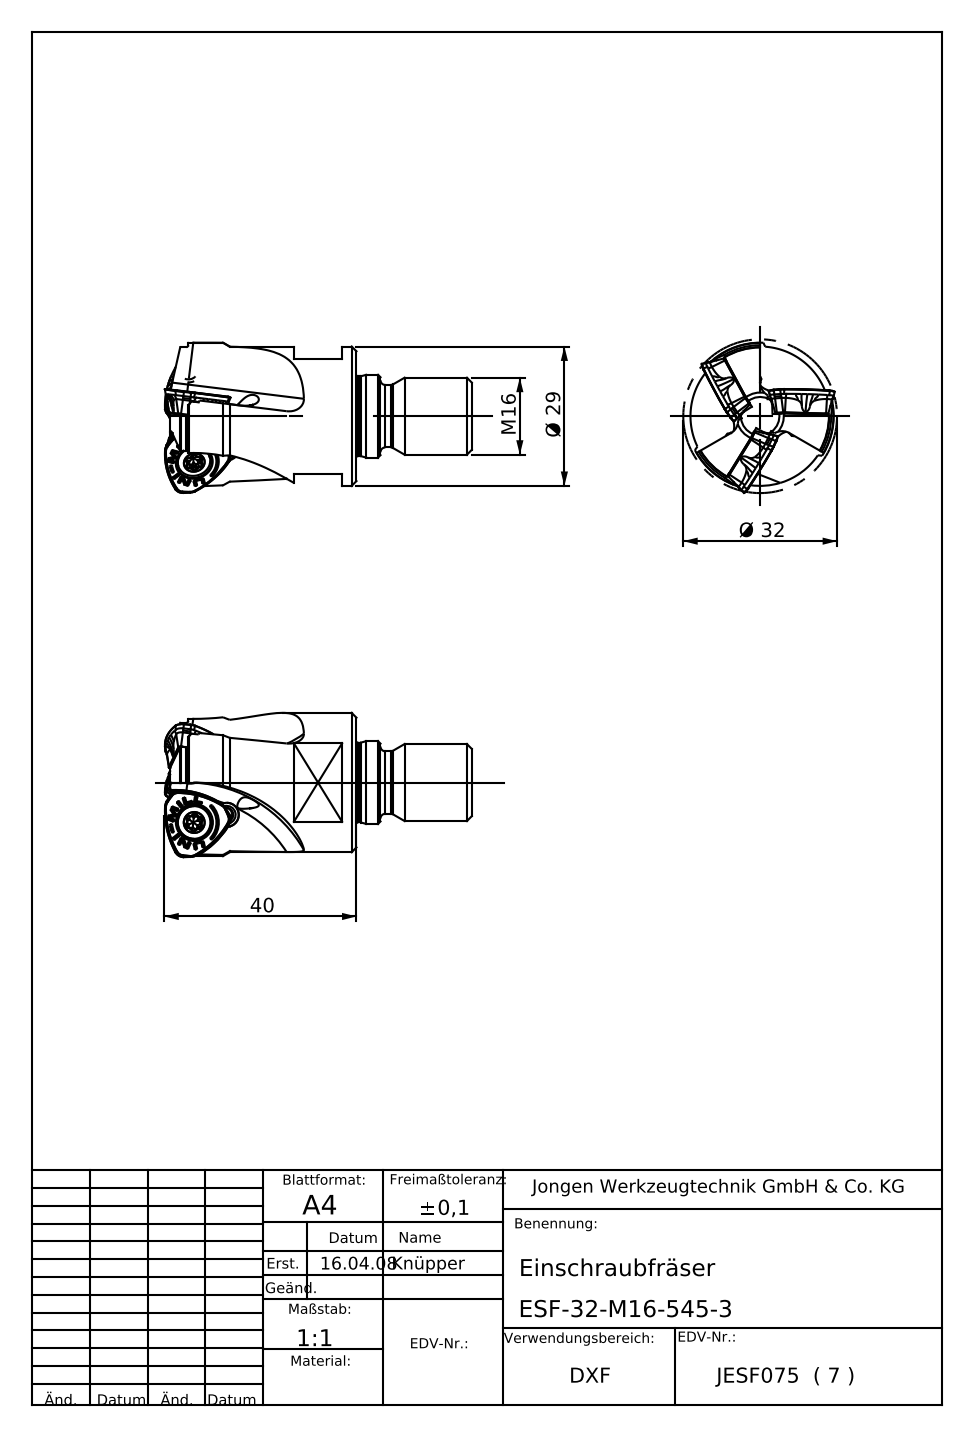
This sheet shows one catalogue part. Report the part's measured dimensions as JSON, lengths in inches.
{"part_name": "ESF-32-M16-545-3", "step_written_by": "SolidWorks 2010 (AUTOMOTIVE_DESIGN)", "units": "inches", "bodies": {"solids": 1, "faces": 42, "planar": 4, "cylindrical": 10, "other": 28}, "overall_size": [2.52, 1.26, 1.26], "volume_in3": 1.931, "surface_area_in2": 9.591, "round_bosses_or_shafts": [[1.205, 1], [1.142, 1], [0.677, 1], [0.63, 1], [0.512, 1]], "face_to_face_distances": [0.945, 0.748, 0.197, 2.475, 1.727, 1.53]}
